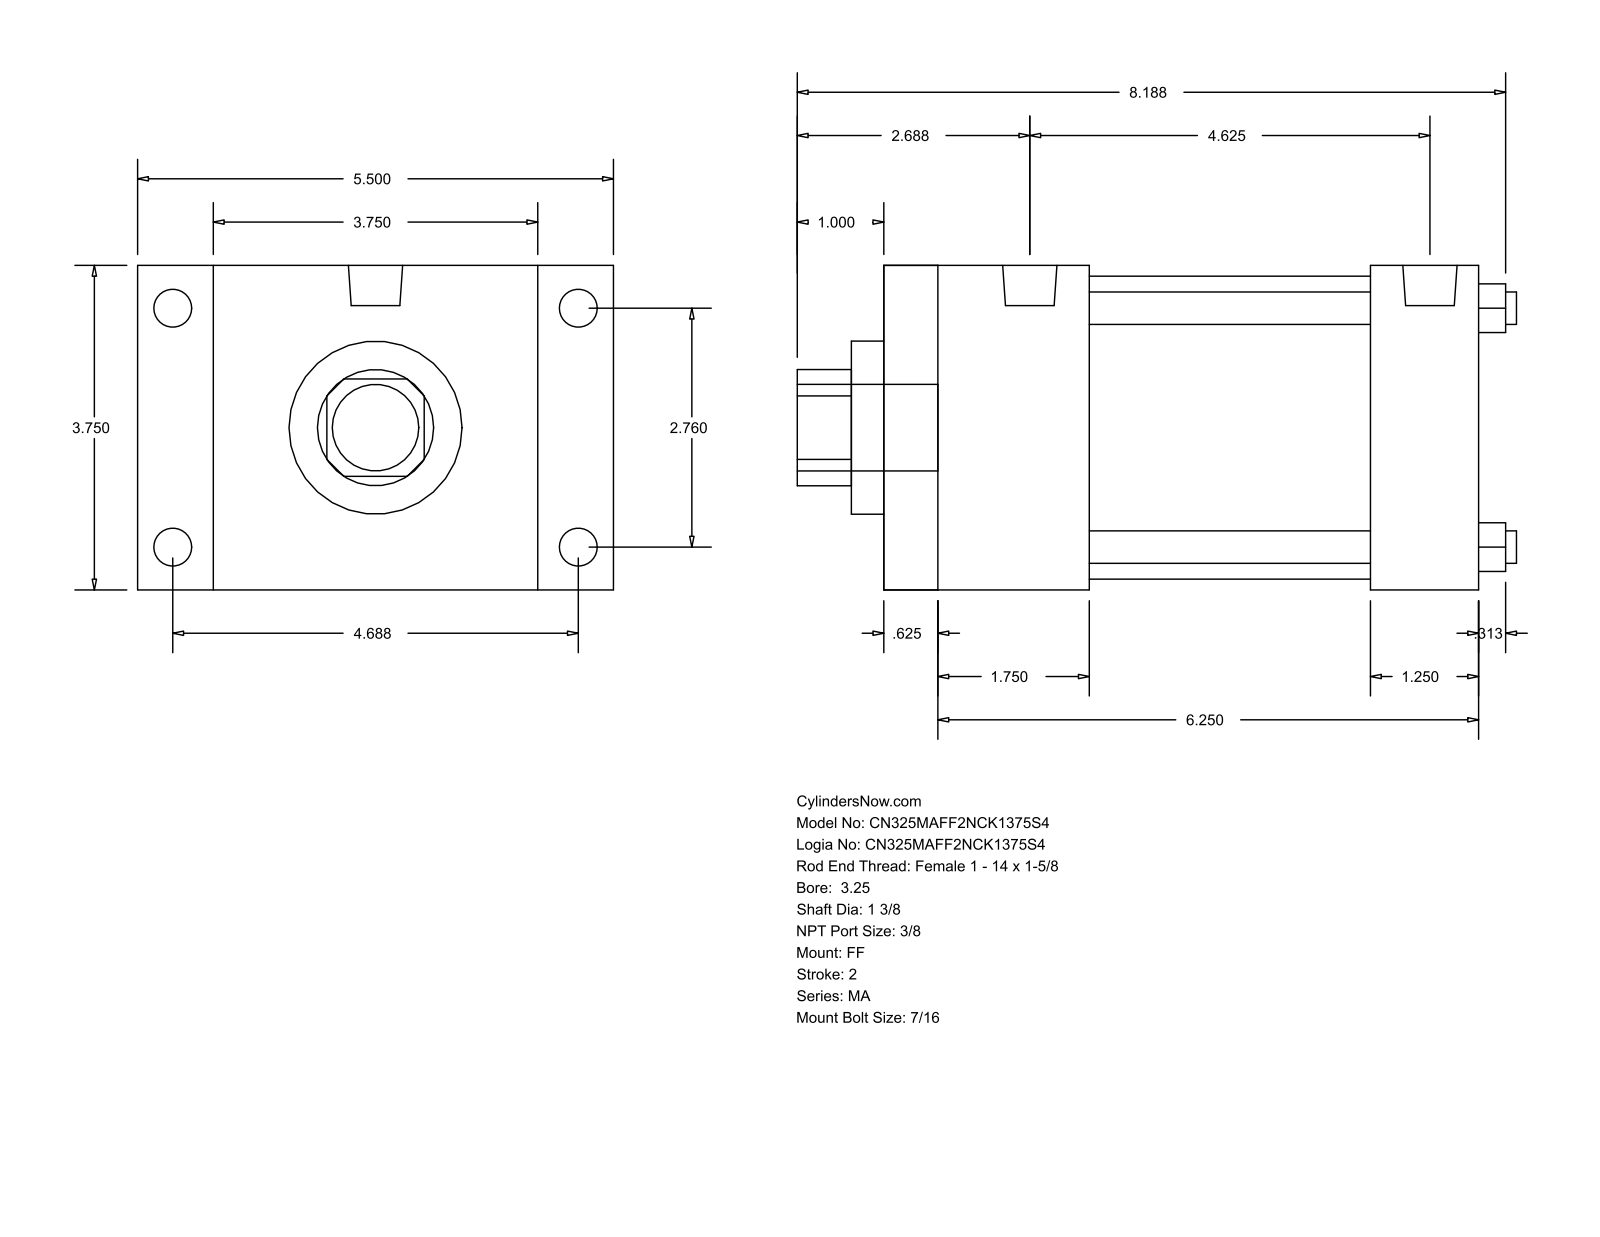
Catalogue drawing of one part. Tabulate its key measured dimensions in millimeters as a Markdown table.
| quantity | value |
| --- | --- |
| part name | MA_FF__0325_1.375 |
| STEP written by | GSSL Pune (CONFIG_CONTROL_DESIGN) |
| units | millimeters |
| bodies | 0 solids, 92 faces (64 planar, 28 cylindrical, 0 other) |
| overall size | 211.14 × 139.7 × 95.25 |
| round holes (diameter × count) | 9.53 × 4, 34.92 × 1, 50.8 × 1, 88.9 × 1 |
| round bosses / shafts (diameter × count) | 11.11 × 8, 15.93 × 2, 25.4 × 1 |
| partial cylindrical surfaces (radius × count) | 17.06 × 1 |
| main face-to-face distances | 95.24, 174.63, 15.87, 158.76, 22.23, 117.47, 60.32, 142.88, 44.45, 127.01 |
| hole center spacings | 49.57, 70.1, 99.14 |
